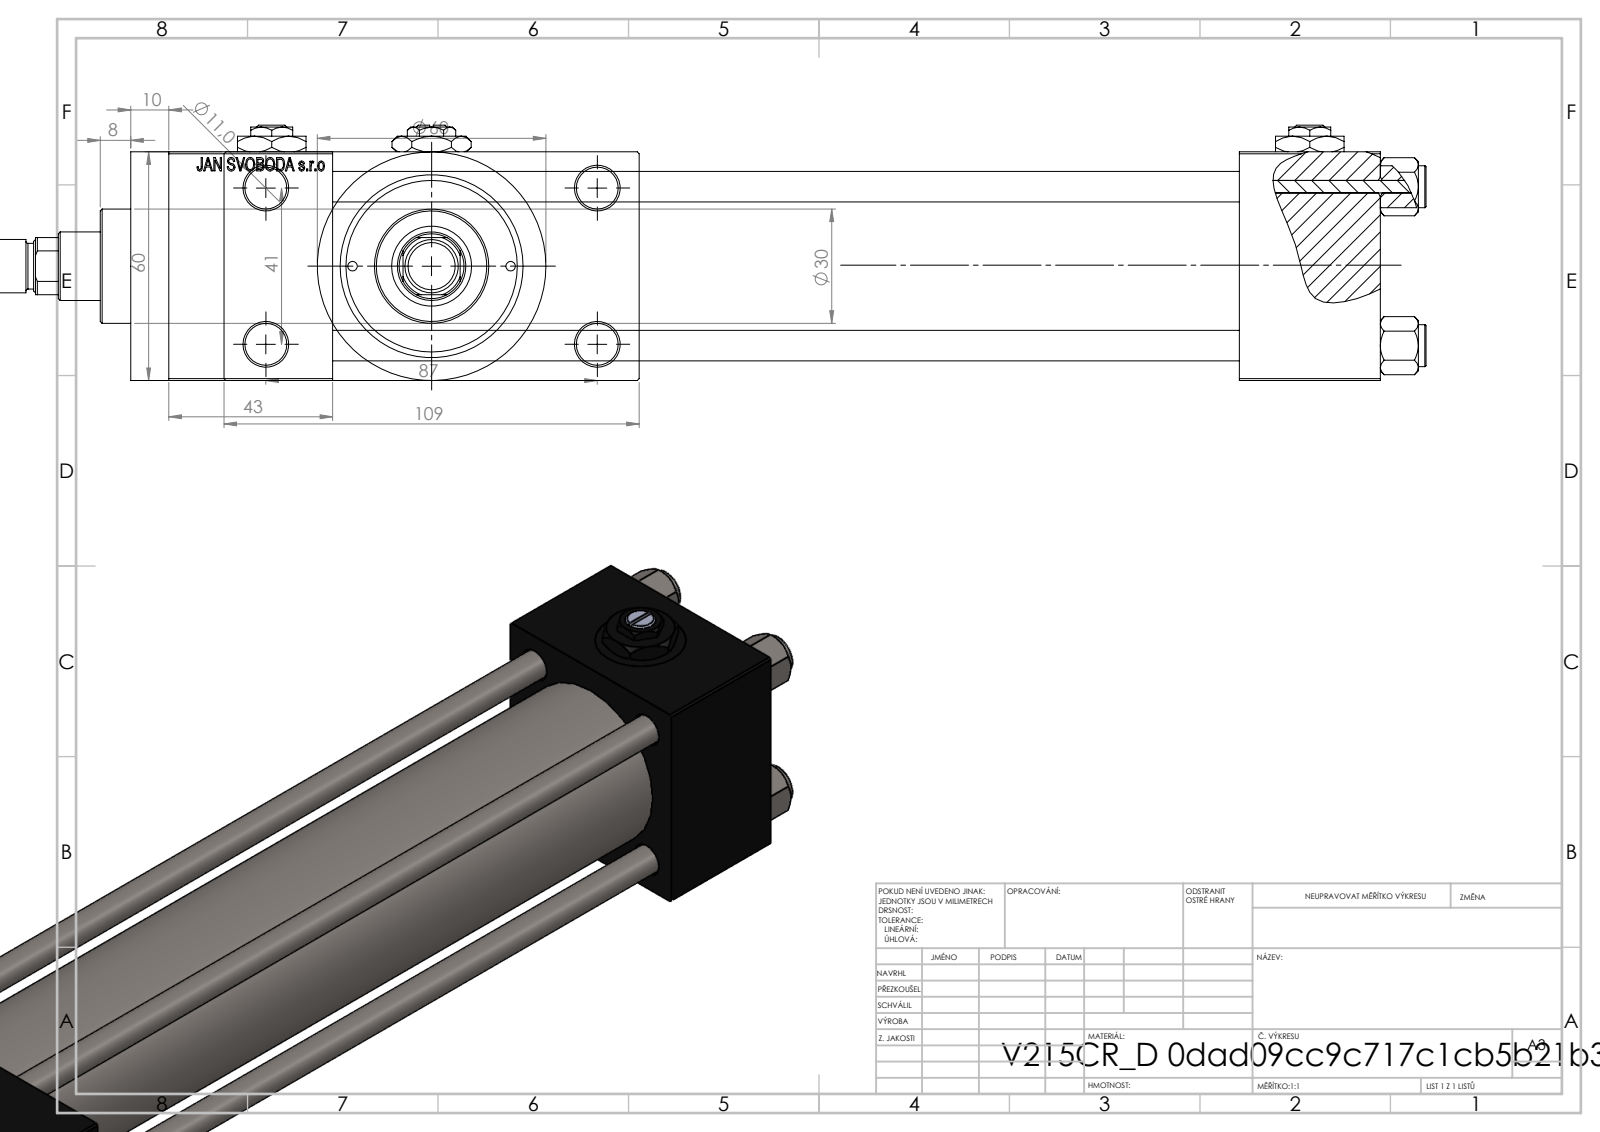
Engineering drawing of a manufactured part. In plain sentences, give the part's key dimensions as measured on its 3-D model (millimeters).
The part is named "V215CR_D_TYCINKA; Zatka_pro_OIL_PORT; V215_VC_A; V215CR_VCP_D (+3 more)". Its 3-D file was written by "SolidWorks 2019 (CONFIG_CONTROL_DESIGN)". It is 14 solids with 1227 faces: 552 planar, 107 cylindrical and 568 other. Overall it measures 383 by 109 by 67 millimeters. Its volume is 667 741 cubic millimeters and its surface area 203 181 square millimeters. Round holes: 4 of diameter 8, 4 of diameter 11, 4 of diameter 16.66, 4 of diameter 24, 3 of diameter 7, 2 of diameter 2.5, 1 of diameter 8.5, 1 of diameter 18, 1 of diameter 21, 1 of diameter 31, 1 of diameter 40, 1 of diameter 45. Round bosses or shafts: 4 of diameter 11, 1 of diameter 60, 1 of diameter 46, 1 of diameter 30, 1 of diameter 14, 1 of diameter 12. Partial cylindrical surfaces (rounded edges, fillets, slot ends): 1 of radius 8.5. The main face-to-face distances are 60, 238, 24.5, 84.5, 37, 275, 43, 318, 281, 53. The hole center spacings are 20.85, 22.65, 29.49, 30.62, 41.7, 46.53, 47.15, 48.09.
